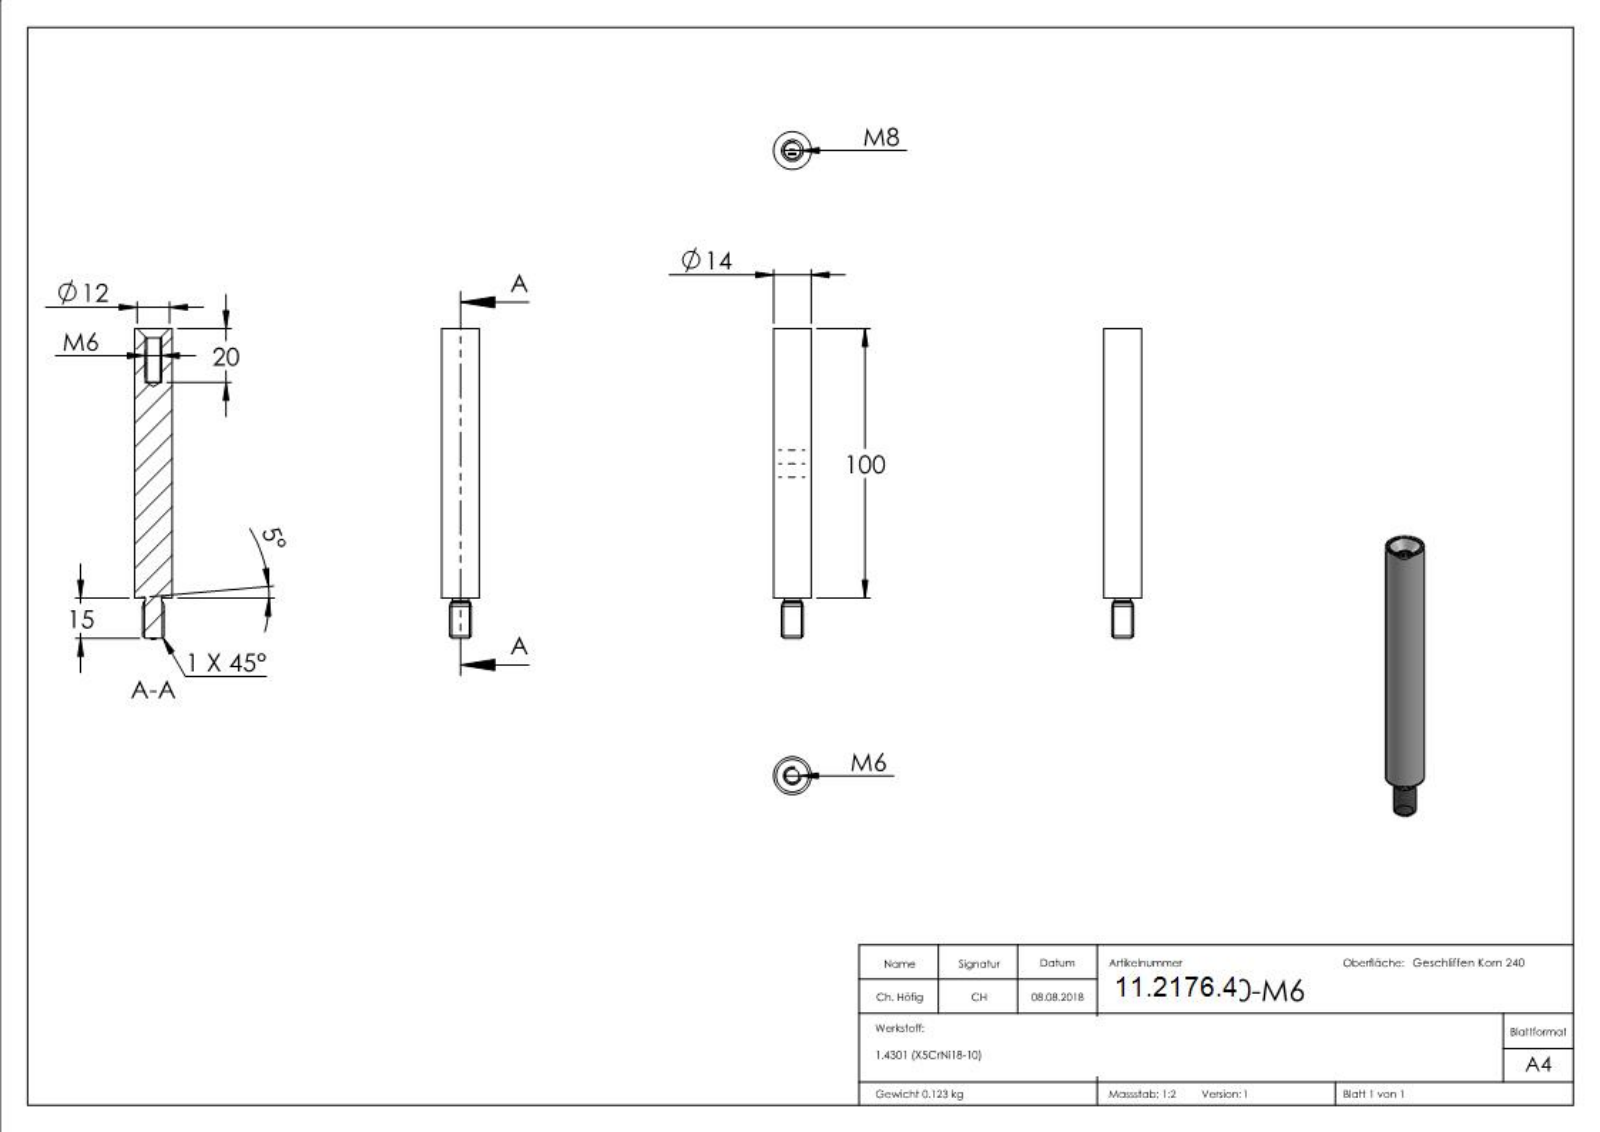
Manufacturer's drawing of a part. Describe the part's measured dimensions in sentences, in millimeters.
The part is named "50237-240-M6". Its 3-D file was written by "SolidWorks 2015 (CONFIG_CONTROL_DESIGN)". It is 1 solid with 284 faces: 147 planar, 8 cylindrical and 129 other. Overall it measures 115 by 14 by 14 millimeters. Its volume is 15 535 cubic millimeters and its surface area 5 393 square millimeters. Round holes: 1 of diameter 5. Round bosses or shafts: 1 of diameter 14, 1 of diameter 8, 1 of diameter 6. The main face-to-face distances are 115, 114.9, 1.44, 0.59, 1.41, 0.33, 1.5, 0.87, 1.32, 0.42.
